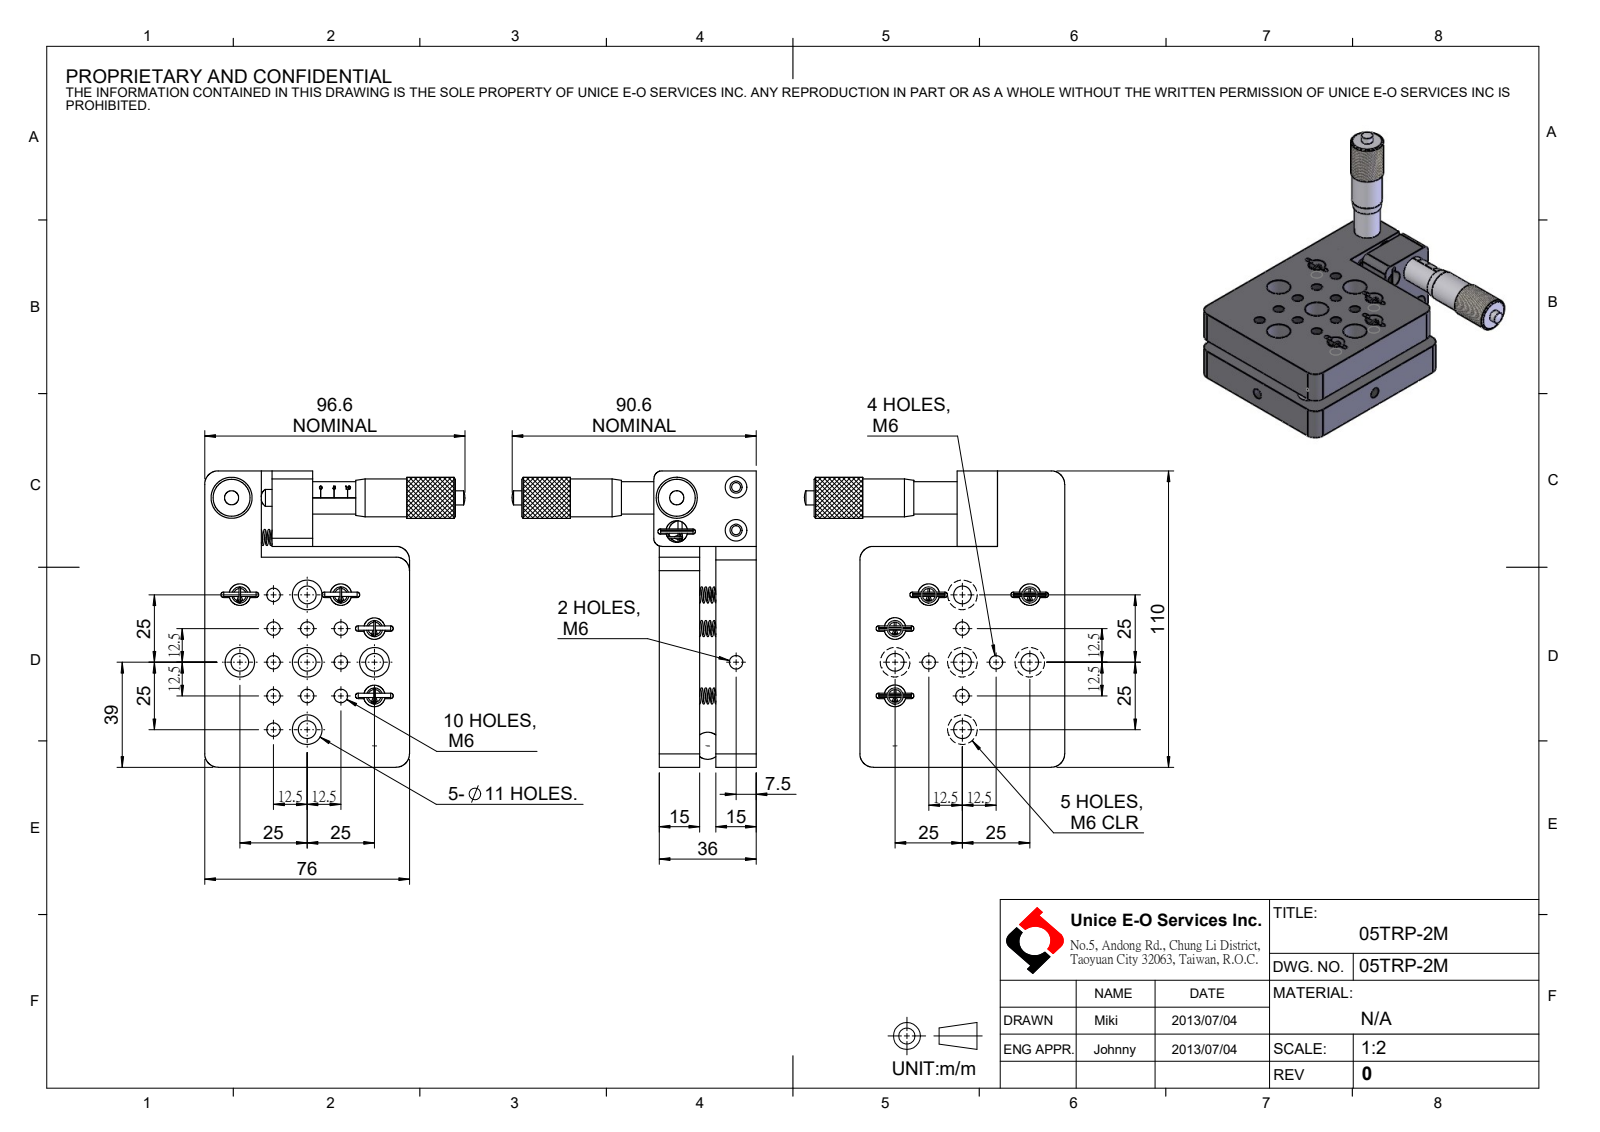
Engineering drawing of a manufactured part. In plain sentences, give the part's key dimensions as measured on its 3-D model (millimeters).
The part is named "05TRP-2M". Its 3-D file was written by "SolidWorks 2016 (CONFIG_CONTROL_DESIGN)". It is 28 solids with 752 faces: 297 planar, 255 cylindrical and 200 other. Overall it measures 110 by 96.62 by 90.66 millimeters. Its volume is 209 169 cubic millimeters and its surface area 70 037 square millimeters. Round holes: 12 of diameter 5, 8 of diameter 1.2, 8 of diameter 8, 5 of diameter 3.3, 5 of diameter 6.6, 5 of diameter 11, 2 of diameter 4.5, 2 of diameter 6.3, 2 of diameter 9.5, 2 of diameter 12.7. Round bosses or shafts: 10 of diameter 0.6, 8 of diameter 1.6, 3 of diameter 4, 2 of diameter 15.2, 2 of diameter 14, 2 of diameter 12, 2 of diameter 9.2, 2 of diameter 5.2. Partial cylindrical surfaces (rounded edges, fillets, slot ends): 13 of radius 1, 6 of radius 3, 5 of radius 5, 2 of radius 5.95. The main face-to-face distances are 15, 21, 36, 6, 76, 28, 25, 51, 4, 82. The hole center spacings are 27.95, 12.5, 17.68, 25, 39.53, 35.36, 37.5, 45.07.
